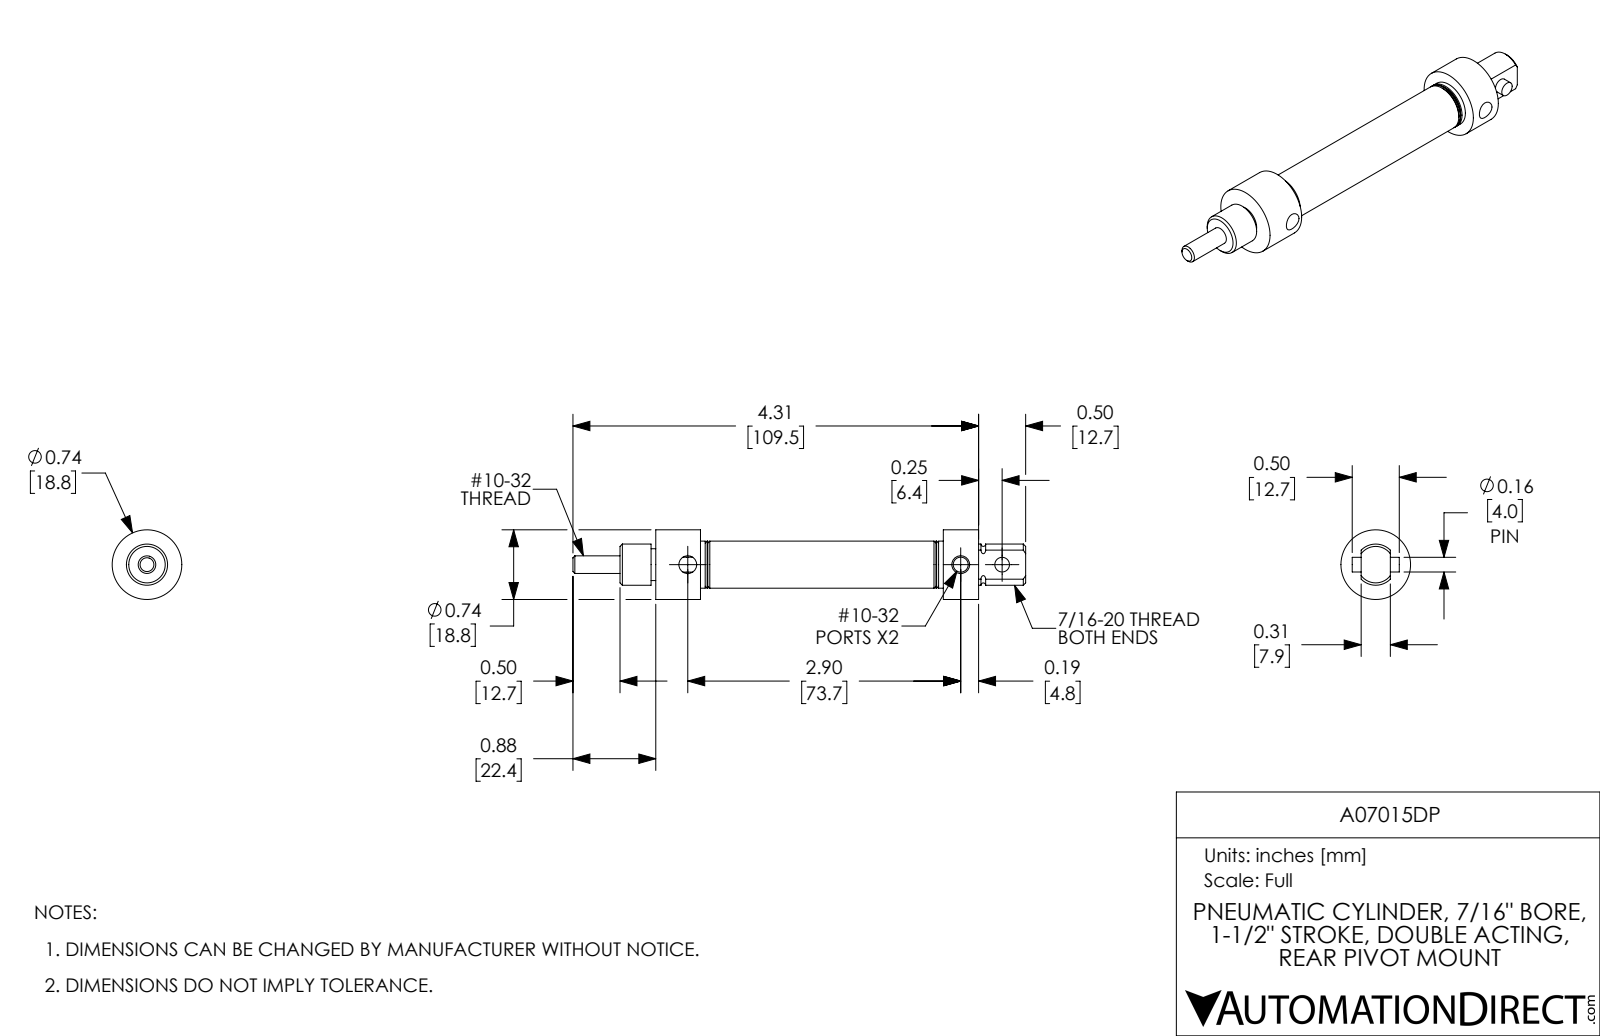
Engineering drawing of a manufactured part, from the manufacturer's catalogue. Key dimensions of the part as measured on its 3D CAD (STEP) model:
Part name (STEP PRODUCT): A07015DP-MainBody; A07015DP-Pin; A07015DP-Rod; A07015DP
STEP written by: SolidWorks 2015 (AUTOMOTIVE_DESIGN)
Units: inches
Bodies: 3 solids, 89 faces (23 planar, 44 cylindrical, 22 other)
Overall size (bounding box): 4.81 × 0.74 × 0.74
Volume: 0.797 in³ · Surface area: 16.03 in²
Round holes (diameter × count): ⌀0.159 ×2, ⌀0.19 ×2, ⌀0.156 ×1, ⌀0.187 ×1
Round bosses / shafts (diameter × count): ⌀0.74 ×1, ⌀0.5 ×1, ⌀0.437 ×1, ⌀0.338 ×1
Main face-to-face distances: 0.715, 2.715, 3.43, 3.055, 0.5, 2.955, 2.24, 0.475, 0.375, 0.34
Hole centre spacings: 0.44, 2.9, 3.34
